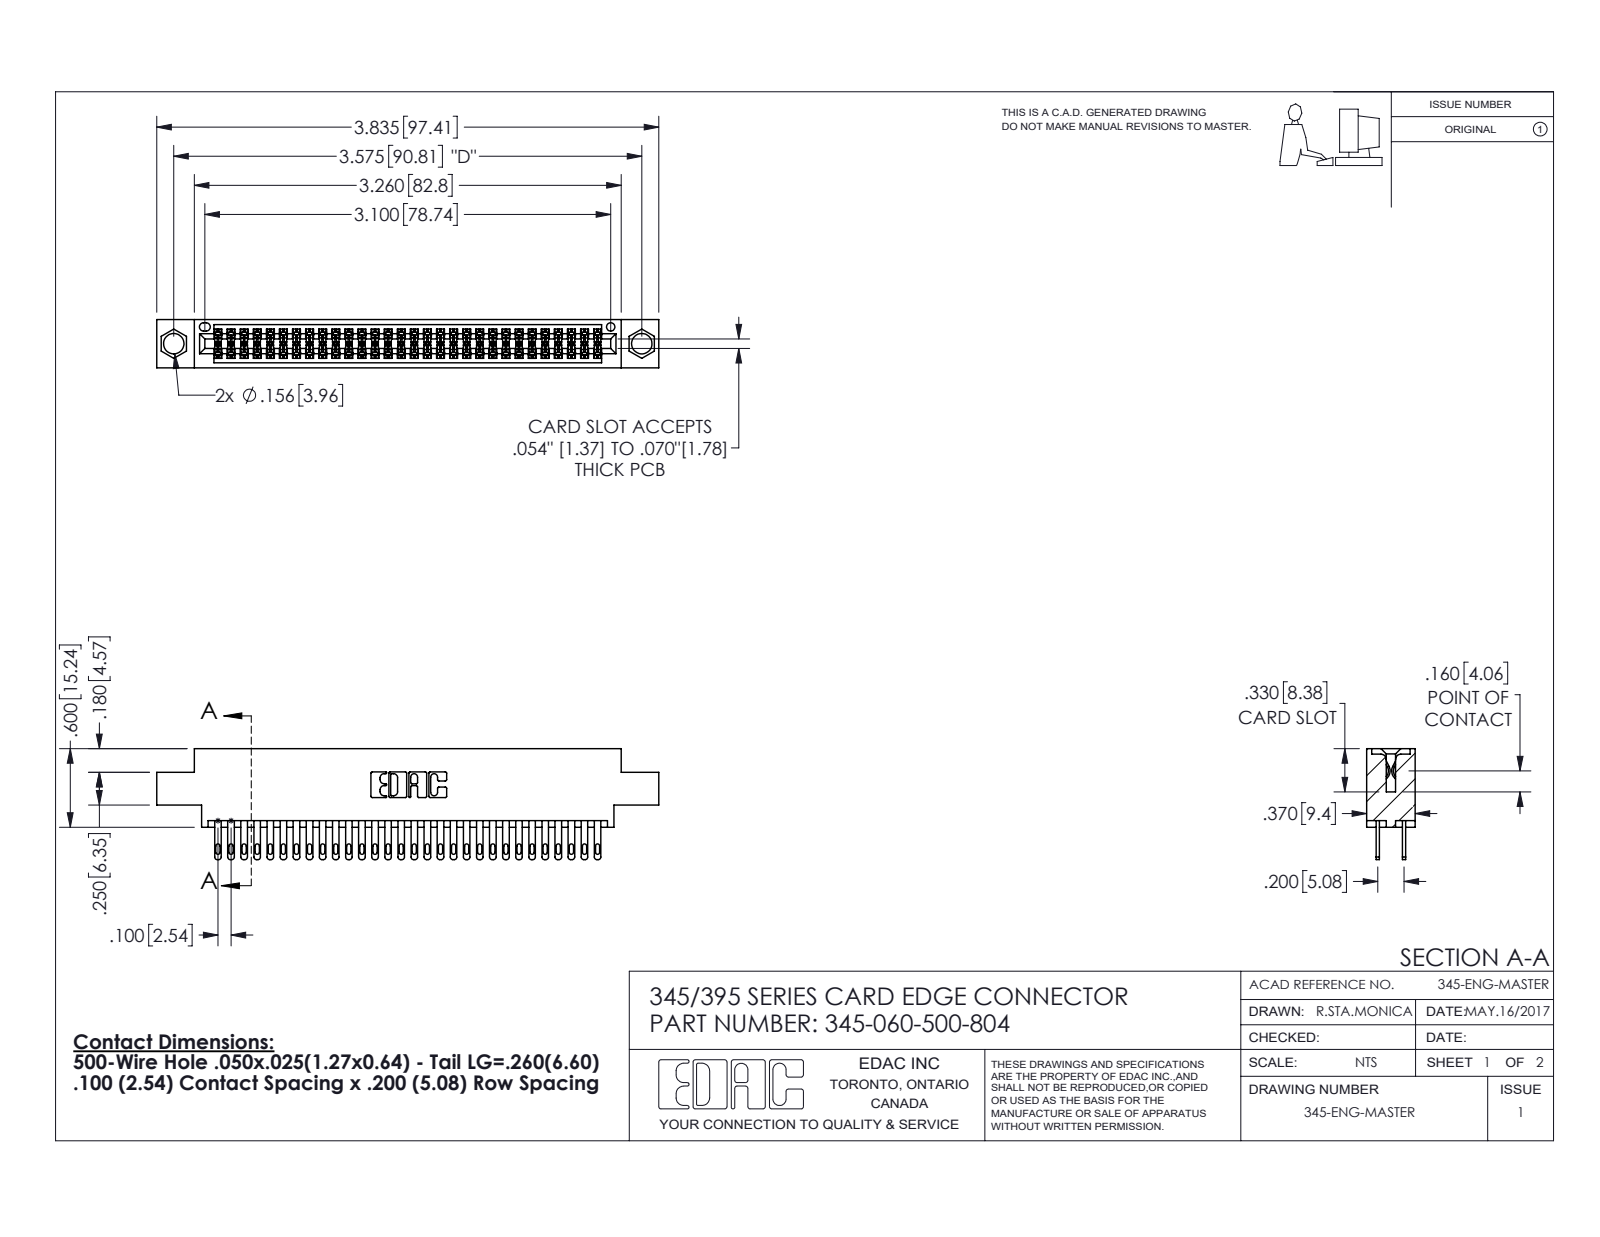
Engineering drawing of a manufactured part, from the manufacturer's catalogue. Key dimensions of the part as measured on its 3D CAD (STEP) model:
Part name (STEP PRODUCT): 345-292-001_345-293-100; 345 Part_0.170 Offset - 0.156 Dia-TI; 345-060-500-804
STEP written by: SolidWorks 2020 (CONFIG_CONTROL_DESIGN)
Units: inches
Bodies: 61 solids, 2904 faces (1718 planar, 1186 cylindrical, 0 other)
Overall size (bounding box): 3.835 × 0.847 × 0.37
Volume: 0.568 in³ · Surface area: 21.92 in²
Round holes (diameter × count): ⌀0.156 ×2, ⌀0.064 ×1
Partial cylindrical surfaces — rounded edges, fillets, slot ends (radius × count): R0.006 ×90, R0.016 ×60, R0.02 ×60, R0.01 ×22, R0.007 ×6, R0.031 ×6, R0.026 ×3, R0.014 ×2
Main face-to-face distances: 0.072, 0.298, 0.2, 0.098, 0.272, 0.025, 0.37, 0.225, 0.175, 0.149
Hole centre spacings: 0.27, 3.34, 3.575
